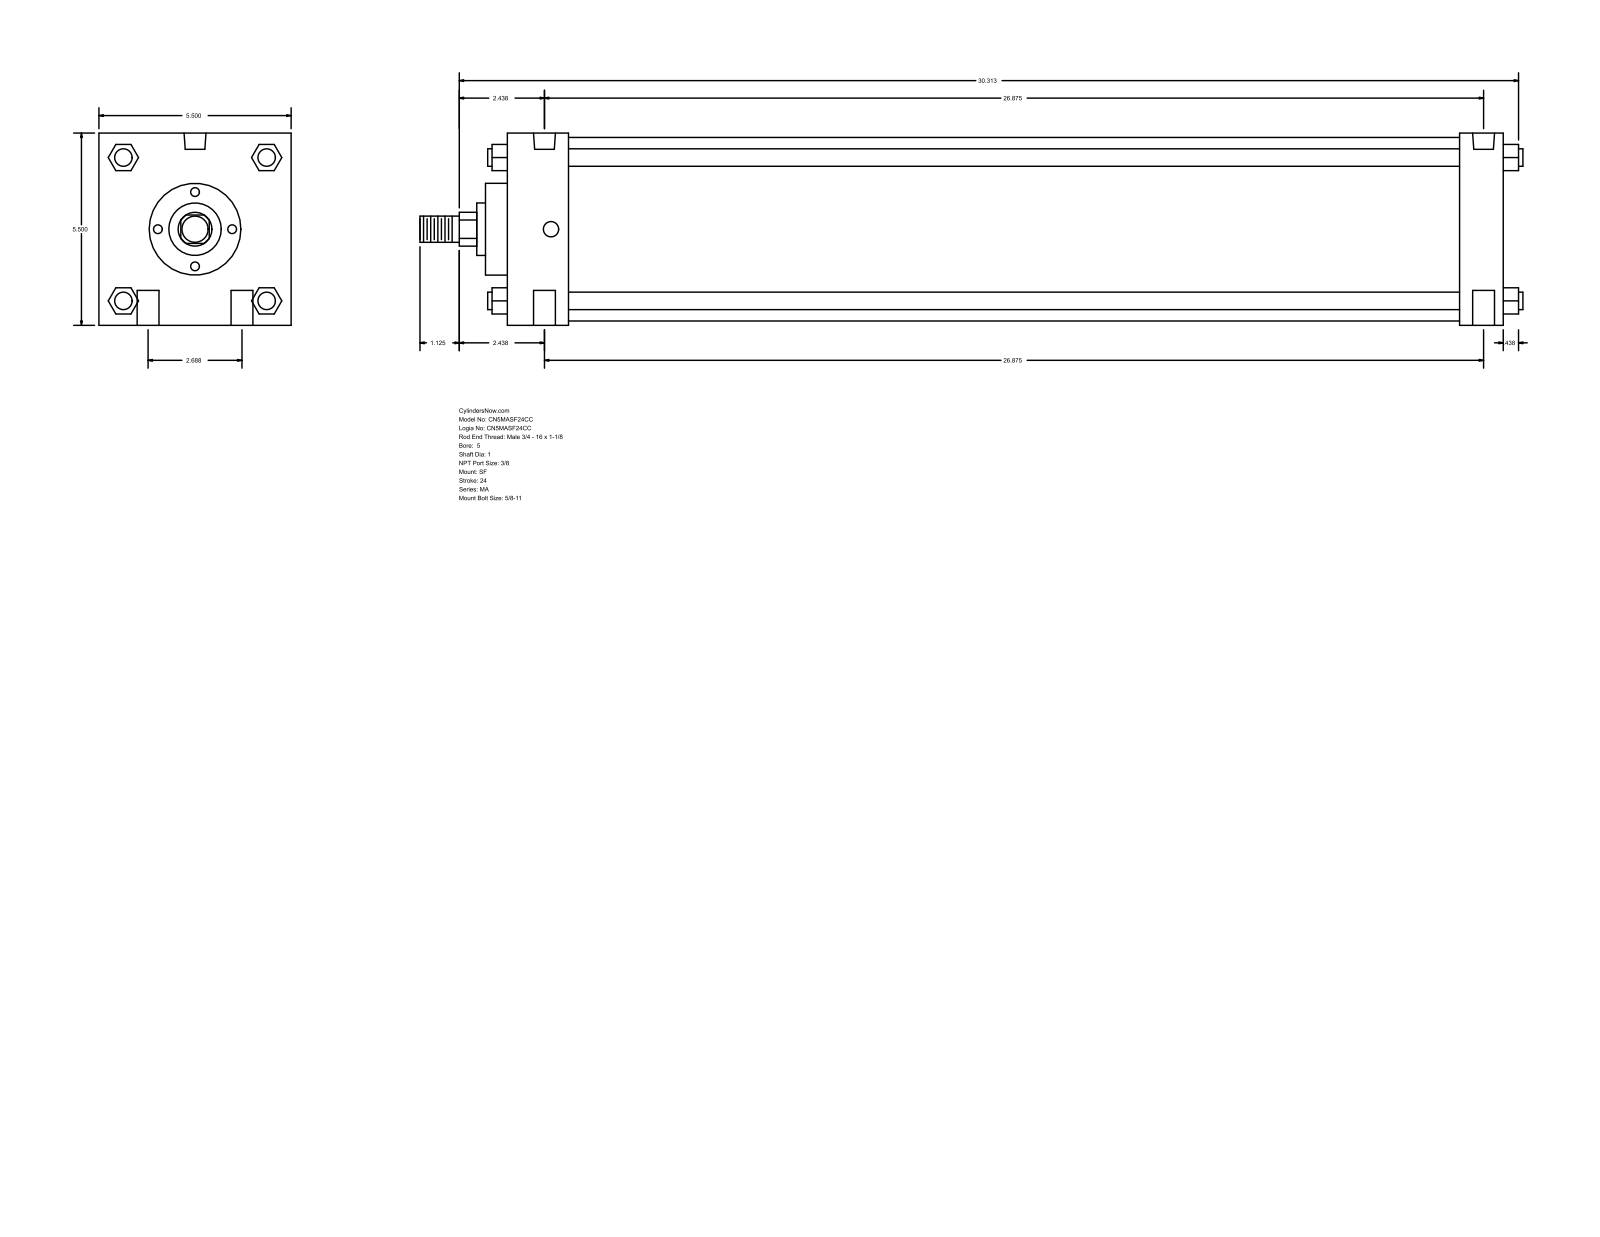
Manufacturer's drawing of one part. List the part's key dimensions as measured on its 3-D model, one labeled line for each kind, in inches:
Part name (STEP PRODUCT): MA_SF__0500_1
STEP written by: GSSL Pune (CONFIG_CONTROL_DESIGN)
Units: inches
Bodies: 0 solids, 126 faces (95 planar, 31 cylindrical, 0 other)
Overall size (bounding box): 31.563 × 5.5 × 5.5
Round holes (diameter × count): ⌀0.625 ×4, ⌀0.437 ×2, ⌀0.627 ×2
Round bosses / shafts (diameter × count): ⌀0.5 ×4, ⌀5.25 ×1, ⌀2.625 ×1, ⌀1.5 ×1, ⌀1 ×1, ⌀0.75 ×1
Partial cylindrical surfaces — rounded edges, fillets, slot ends (radius × count): R0.484 ×1
Main face-to-face distances: 5.5, 28.5, 1.75, 27.25, 25.5, 26.75, 1.25, 0.625, 2.375, 27.875
Hole centre spacings: 1.344, 26.909, 26.875, 2.687, 27.009, 26.5
